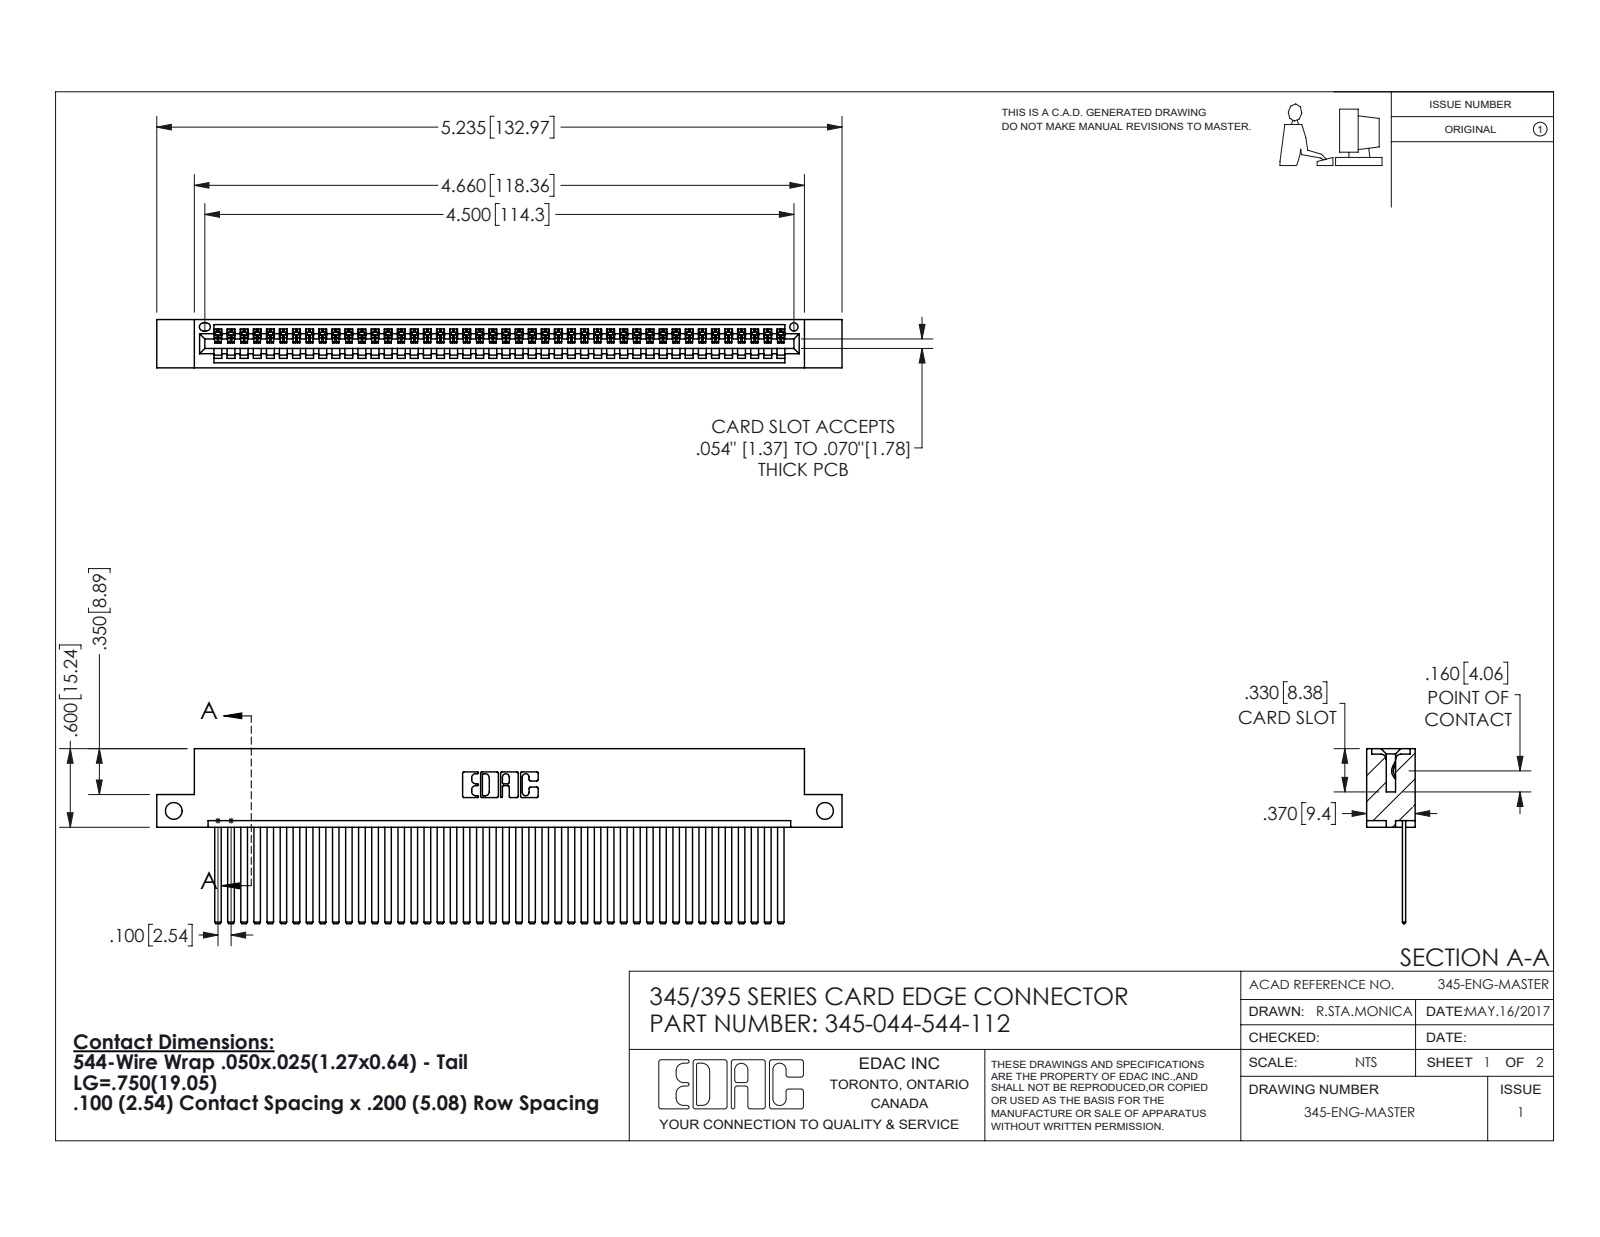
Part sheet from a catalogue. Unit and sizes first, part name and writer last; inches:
Units: inches
Overall size (bounding box): 5.235 × 1.337 × 0.37
Round holes (diameter × count): ⌀0.128 ×2, ⌀0.064 ×1
Partial cylindrical surfaces — rounded edges, fillets, slot ends (radius × count): R0.006 ×88, R0.01 ×22, R0.007 ×6, R0.031 ×6, R0.026 ×3, R0.031 ×2, R0.04 ×2, R0.014 ×1
Main face-to-face distances: 0.072, 0.298, 0.025, 0.098, 0.272, 0.37, 0.2, 0.225, 0.149, 0.072
Hole centre spacings: 4.975
Volume: 0.797 in³ · Surface area: 29.11 in²
Bodies: 45 solids, 2414 faces (1664 planar, 750 cylindrical, 0 other)
Part name (STEP PRODUCT): 345-044-544-112; 345-292-001_345-293-144; 345 Part_Flush Mounting Lugs - Side Mount
STEP written by: SolidWorks 2016 (CONFIG_CONTROL_DESIGN)
